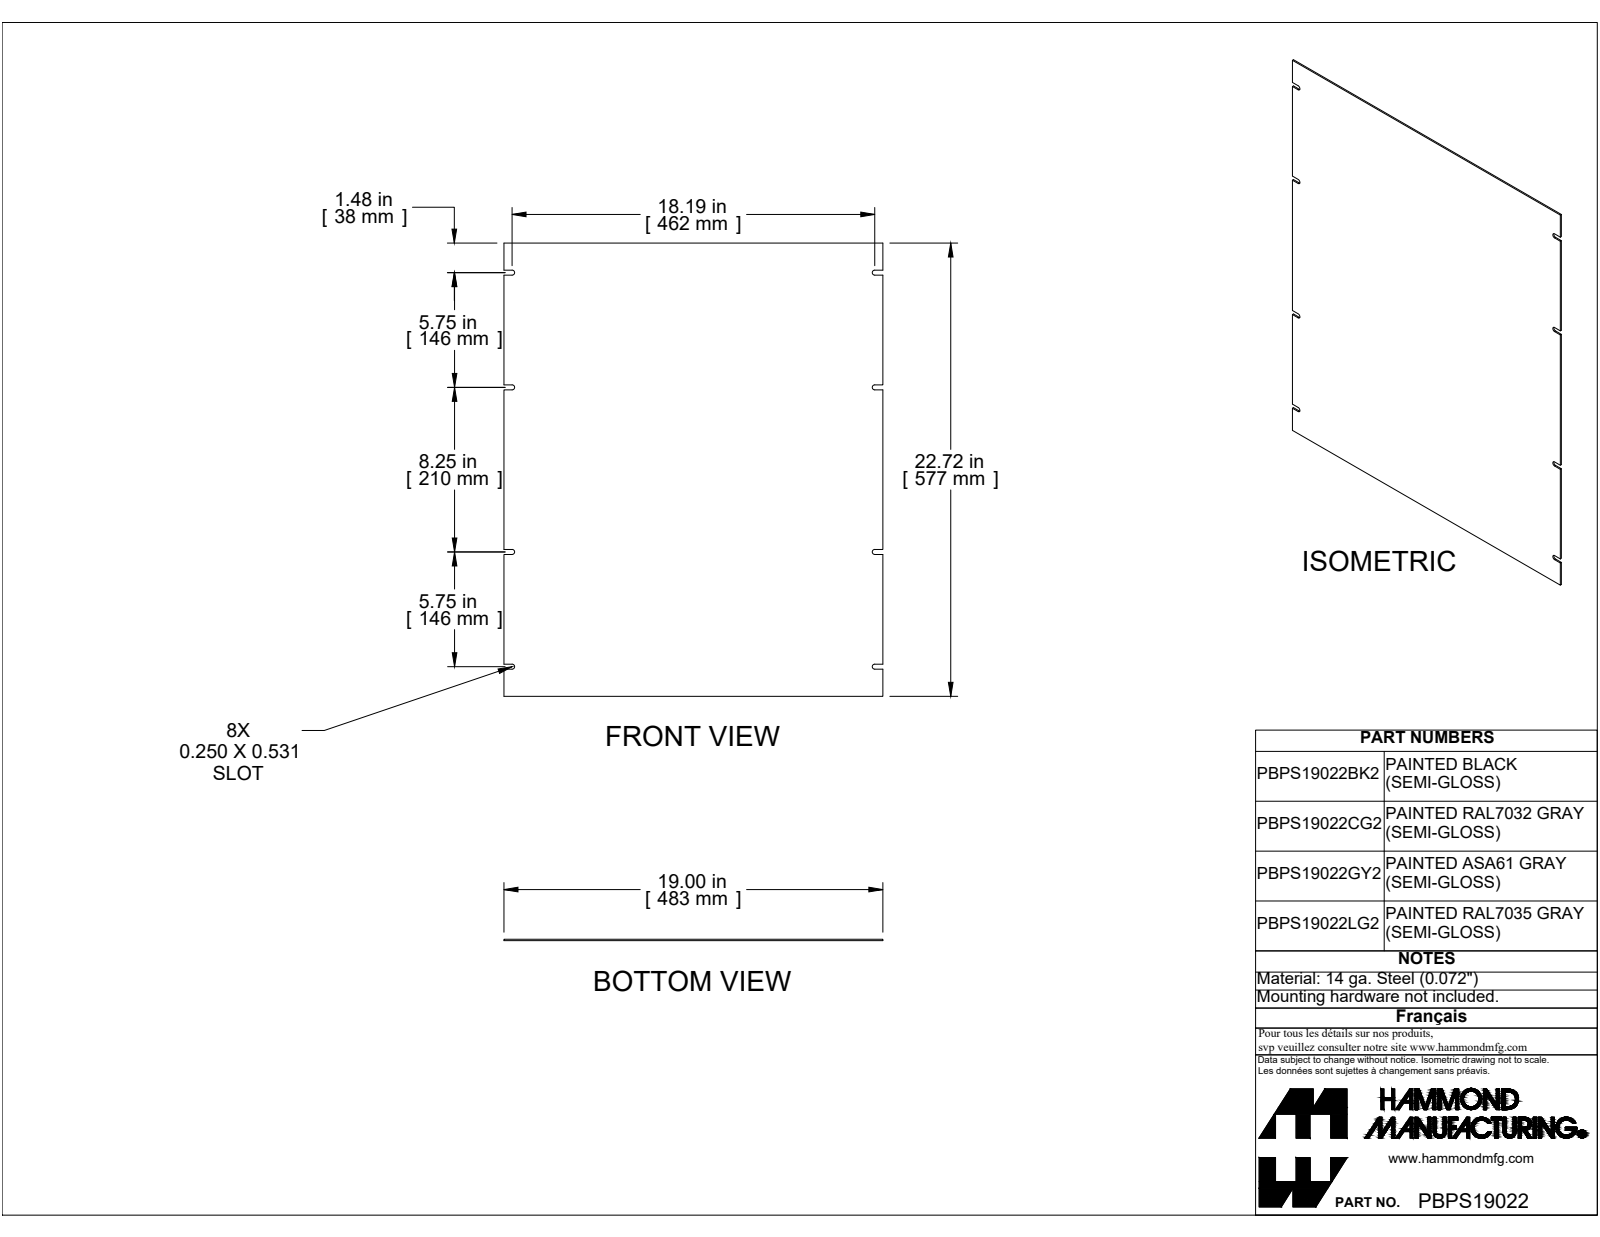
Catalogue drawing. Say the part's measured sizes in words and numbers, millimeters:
The part is named "PBPS19022GY2". Its 3-D file was written by "SolidWorks 2019 (CONFIG_CONTROL_DESIGN)". It is 1 solid with 38 faces: 30 planar, 8 cylindrical and 0 other. Overall it measures 577 by 482.6 by 1.8 millimeters. Its volume is 508 200 cubic millimeters and its surface area 559 900 square millimeters. Partial cylindrical surfaces (rounded edges, fillets, slot ends): 8 of radius 3.2. The main face-to-face distances are 1.8, 482.6, 577, 6.4, 146.1, 355.6, 180.6, 396.5, 186.9, 390.1.
